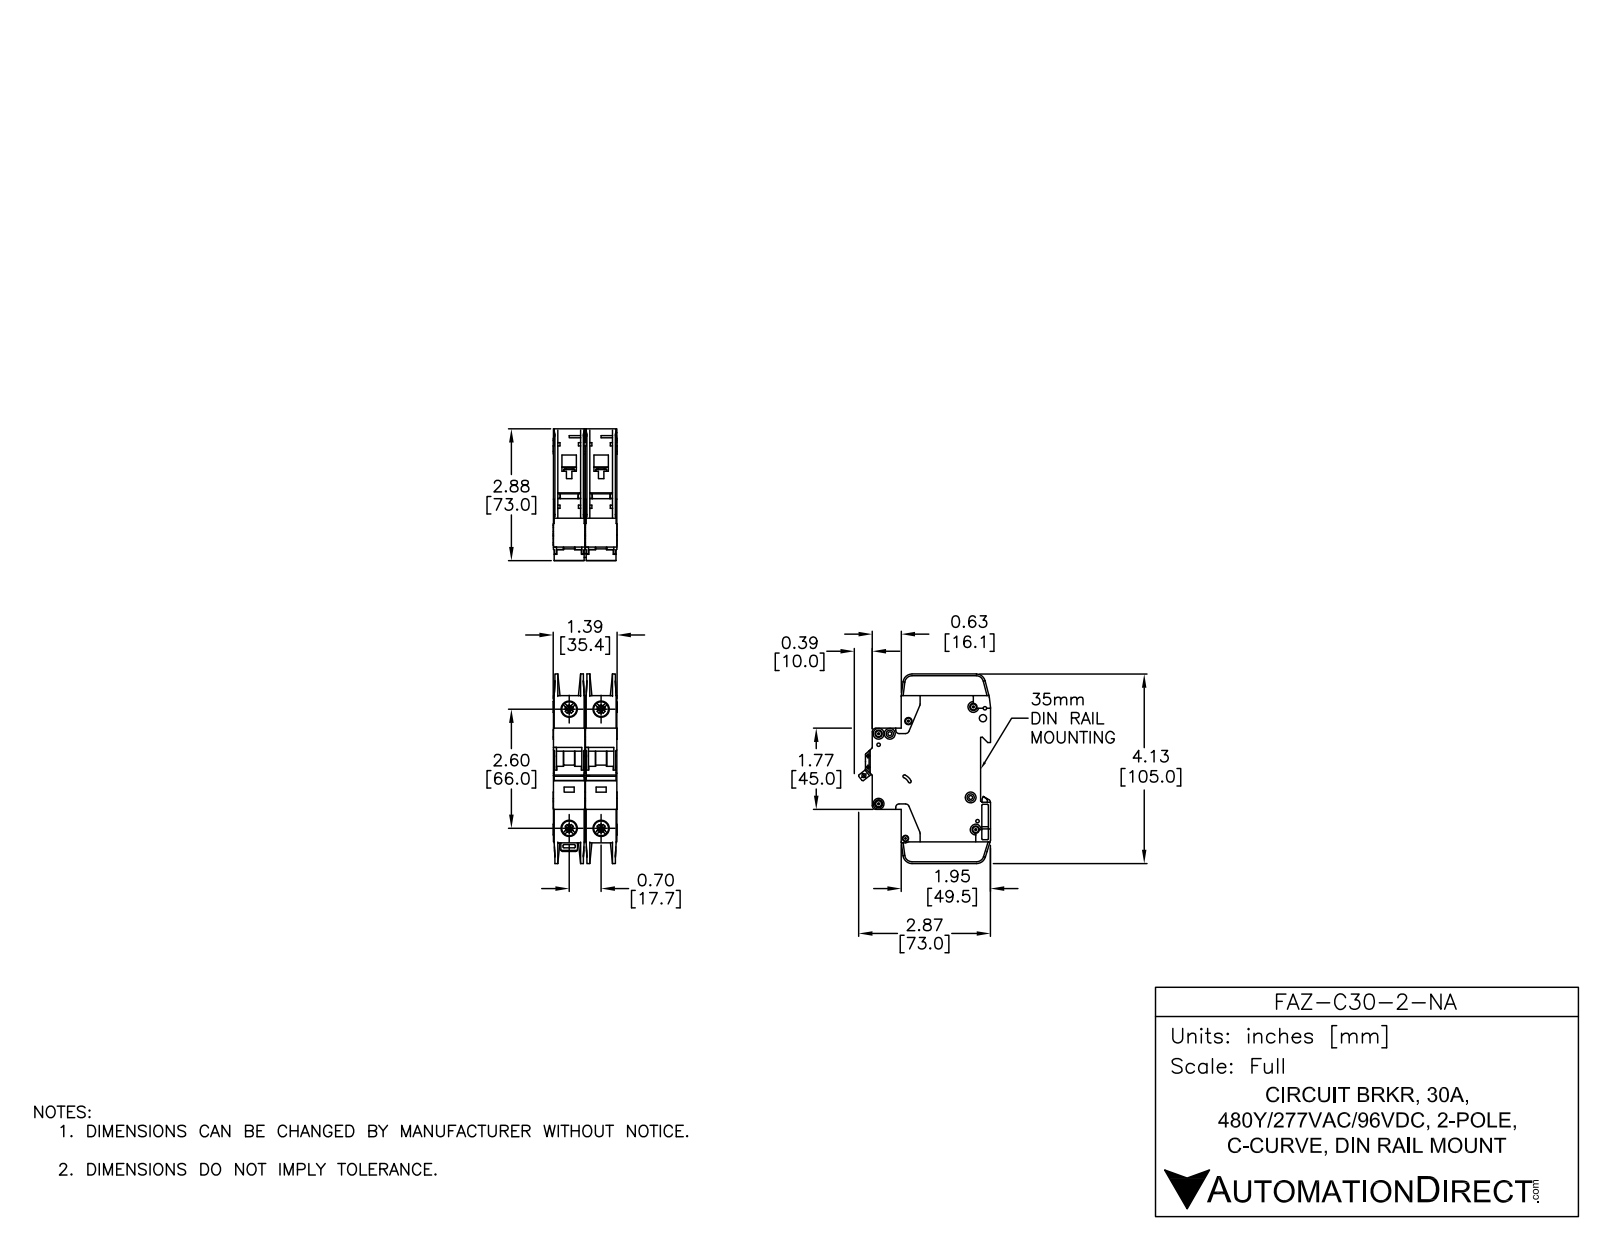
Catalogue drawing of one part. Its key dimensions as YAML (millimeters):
part_name: "FAZ-C30-2-NA"
step_written_by: "SolidWorks 2014 (AUTOMOTIVE_DESIGN)"
units: millimeters
bodies: {solids: 6, faces: 1568, planar: 818, cylindrical: 526, other: 224}
overall_size: [105, 73.04, 35.4]
volume: 155390
surface_area: 49479
round_holes:
  - {diameter: 3.6, count: 7}
  - {diameter: 7.15, count: 4}
  - {diameter: 8.2, count: 4}
  - {diameter: 1.09, count: 2}
  - {diameter: 1.5, count: 2}
  - {diameter: 4, count: 2}
  - {diameter: 1.9, count: 1}
  - {diameter: 2.15, count: 1}
  - {diameter: 2.2, count: 1}
  - {diameter: 2.55, count: 1}
  - {diameter: 3.3, count: 1}
  - {diameter: 3.4, count: 1}
round_bosses_or_shafts:
  - {diameter: 6, count: 7}
  - {diameter: 2.5, count: 2}
partial_cylinders:
  - {radius: 0.25, count: 47}
  - {radius: 0.5, count: 24}
  - {radius: 1, count: 18}
  - {radius: 2, count: 12}
  - {radius: 5, count: 5}
  - {radius: 1.8, count: 4}
  - {radius: 4, count: 4}
  - {radius: 0.2, count: 2}
face_to_face_distances: [17.7, 17.5, 0.7, 15.05, 2.45, 1.75, 15.75, 13.3, 35.2, 17]
hole_center_spacings: [6.2, 17.7, 66, 68.33, 5.19, 6.1, 8.19, 8.56]
